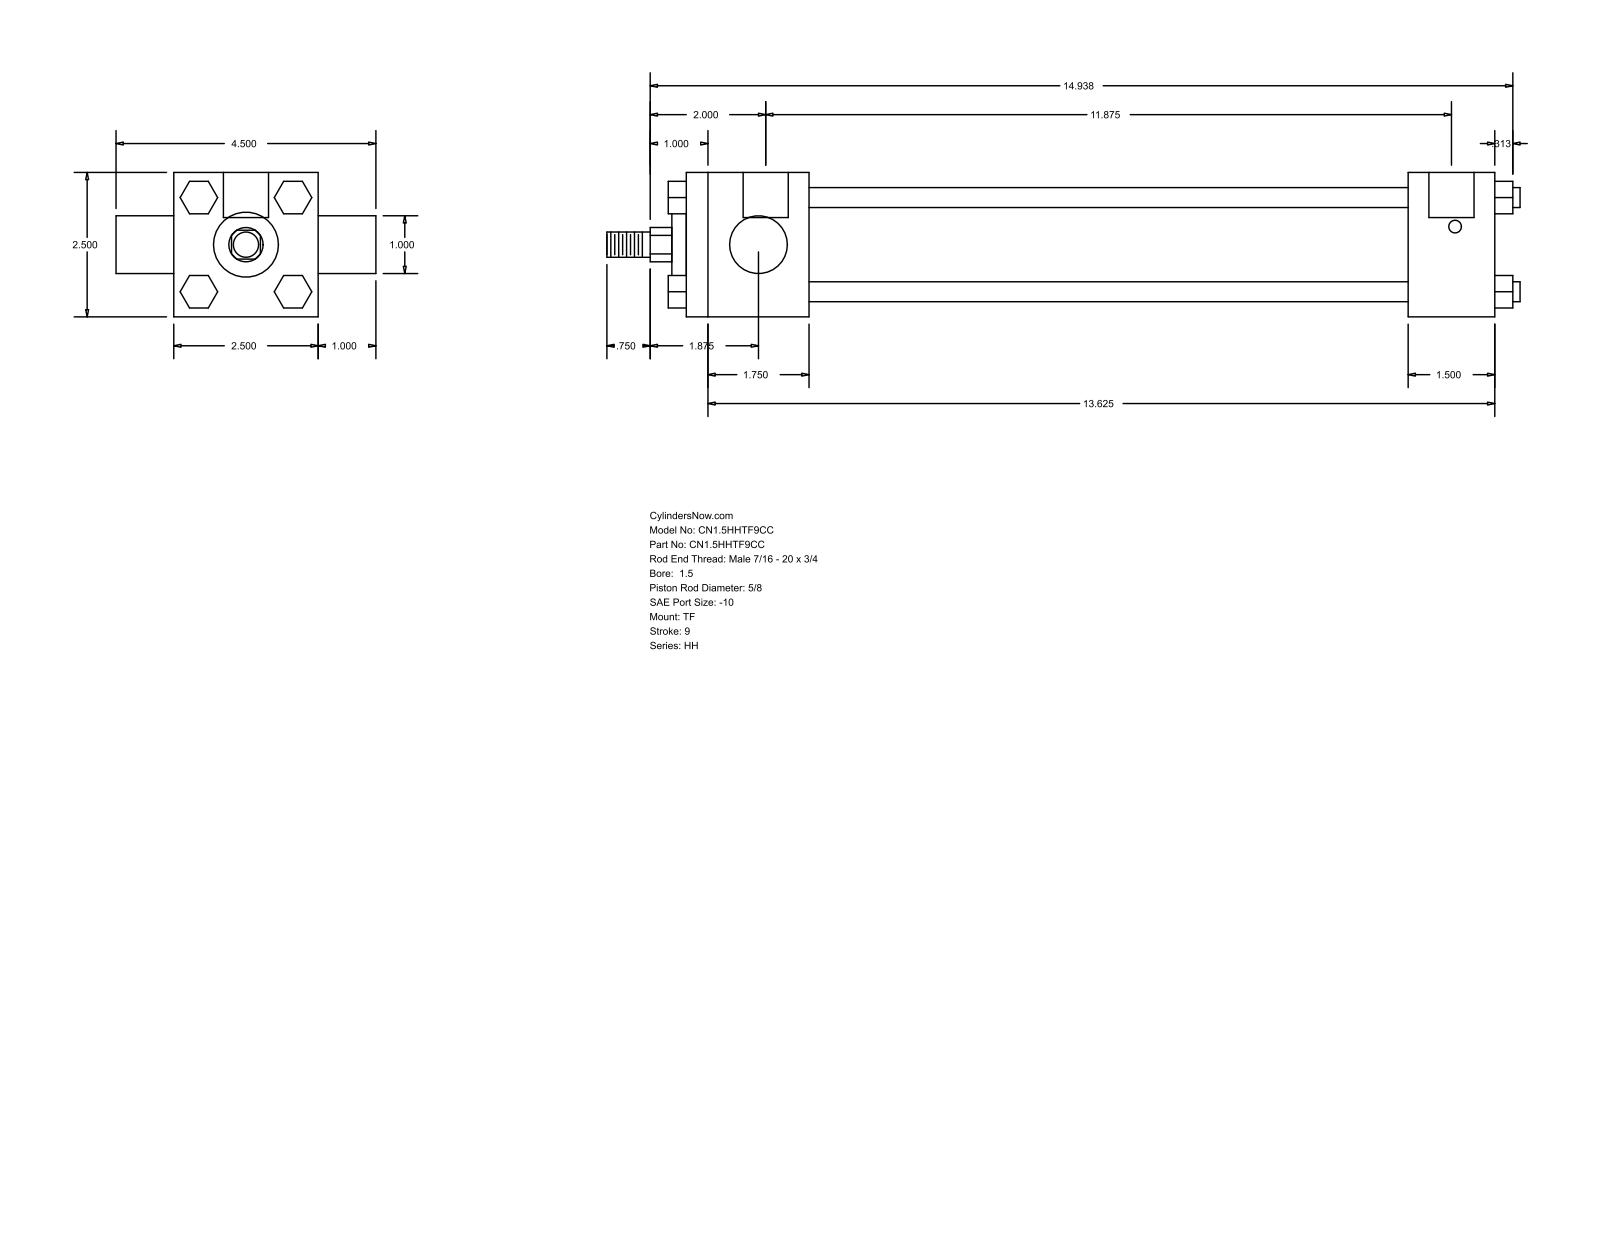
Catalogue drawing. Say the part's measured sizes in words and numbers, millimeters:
The part is named "HH_TF__0150_0.625". Its 3-D file was written by "GSSL Pune (CONFIG_CONTROL_DESIGN)". It is 0 solids with 120 faces: 92 planar, 28 cylindrical and 0 other. Overall it measures 401.64 by 114.3 by 63.5 millimeters. Round holes: 3 of diameter 5.56, 2 of diameter 19.84. Round bosses or shafts: 4 of diameter 8.76, 1 of diameter 44.45, 1 of diameter 28.57, 1 of diameter 25.4, 1 of diameter 15.88, 1 of diameter 11.11. Partial cylindrical surfaces (rounded edges, fillets, slot ends): 1 of radius 7.54. The main face-to-face distances are 63.5, 355.6, 38.1, 53.97, 301.63, 317.5, 263.53, 25.4, 88.9, 20.7. The hole center spacings are 1.58, 1.59, 301.63, 303.21, 303.22, 304.8.
